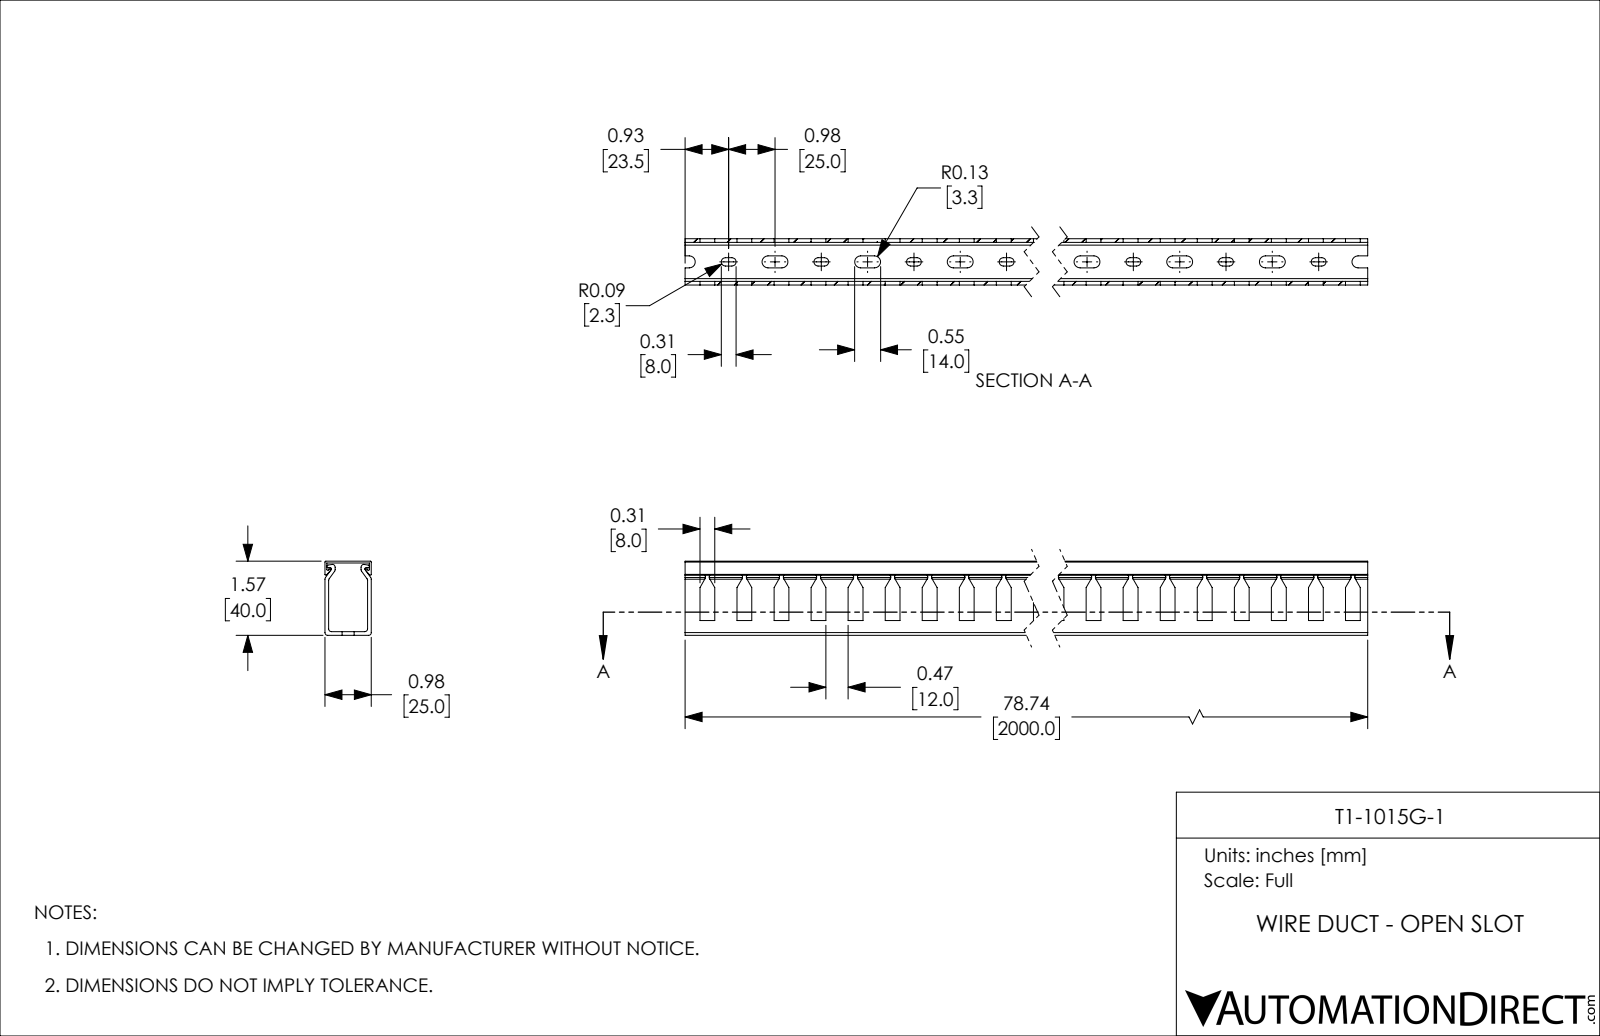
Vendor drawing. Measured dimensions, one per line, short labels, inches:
name: T1-1015G-1
written by: SolidWorks 2021 (CONFIG_CONTROL_DESIGN)
unit: in
bodies: 2 solids, 945 faces (514 planar, 431 cylindrical, 0 other)
size: 78.74 × 1.575 × 0.984
volume: 29.46 in³; area: 888.1 in²
rounds: 80× R0.089, 80× R0.128, 12× R0.059, 8× R0.02, 6× R0.03
face distances: 0.079, 0.906, 0.039, 0.984, 0.827, 1.575, 1.535, 1.457, 1.496, 0.945
